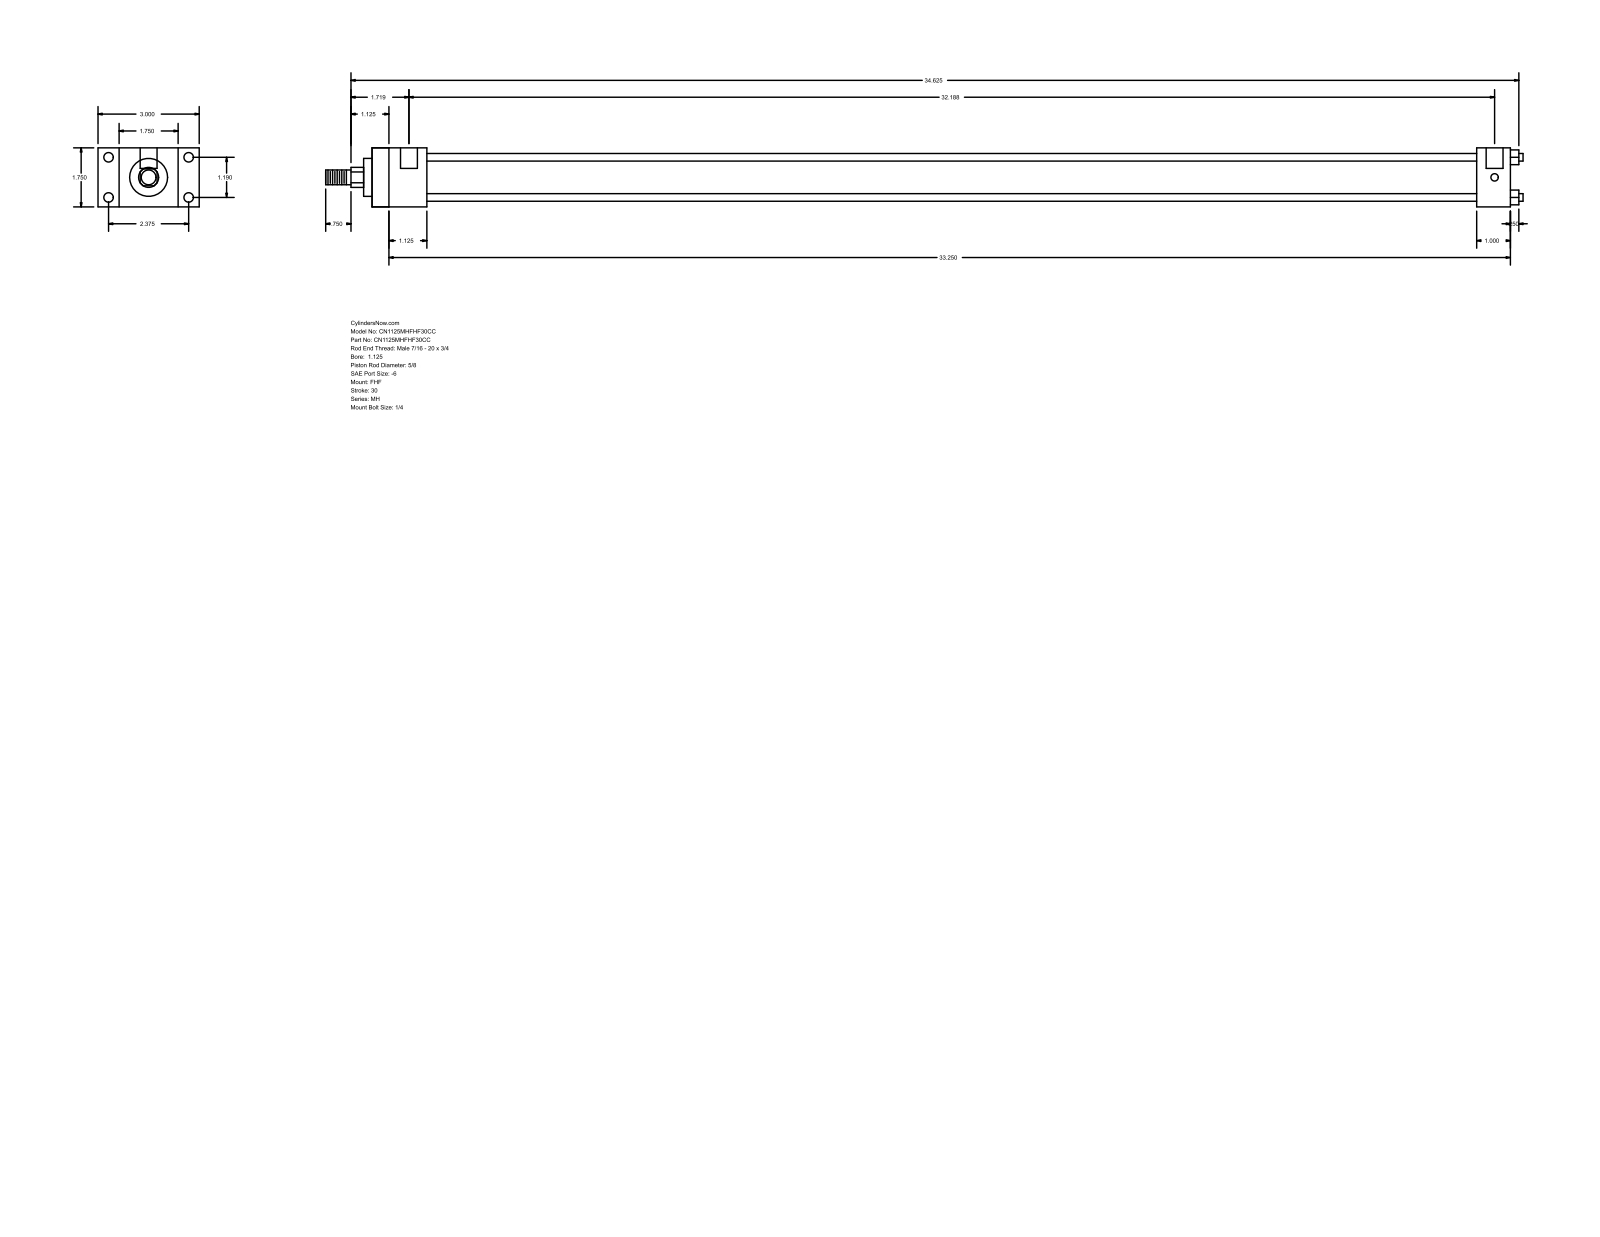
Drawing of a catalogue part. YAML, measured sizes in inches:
part_name: "MH_FHF__0112_0.625"
step_written_by: "GSSL Pune (CONFIG_CONTROL_DESIGN)"
units: inches
bodies: {solids: 0, faces: 88, planar: 60, cylindrical: 28, other: 0}
overall_size: [35.5, 3, 1.75]
round_holes:
  - {diameter: 0.219, count: 4}
  - {diameter: 0.281, count: 4}
  - {diameter: 0.5, count: 2}
round_bosses_or_shafts:
  - {diameter: 0.225, count: 4}
  - {diameter: 1.375, count: 1}
  - {diameter: 1.125, count: 1}
  - {diameter: 0.625, count: 1}
  - {diameter: 0.437, count: 1}
partial_cylinders:
  - {radius: 0.297, count: 1}
face_to_face_distances: [1.75, 0.625, 2.375, 1.625, 3, 33.75, 32.125, 32.75, 31.125, 1]
hole_center_spacings: [1.19, 2.375, 2.656, 32.063, 0.125, 32.187]
